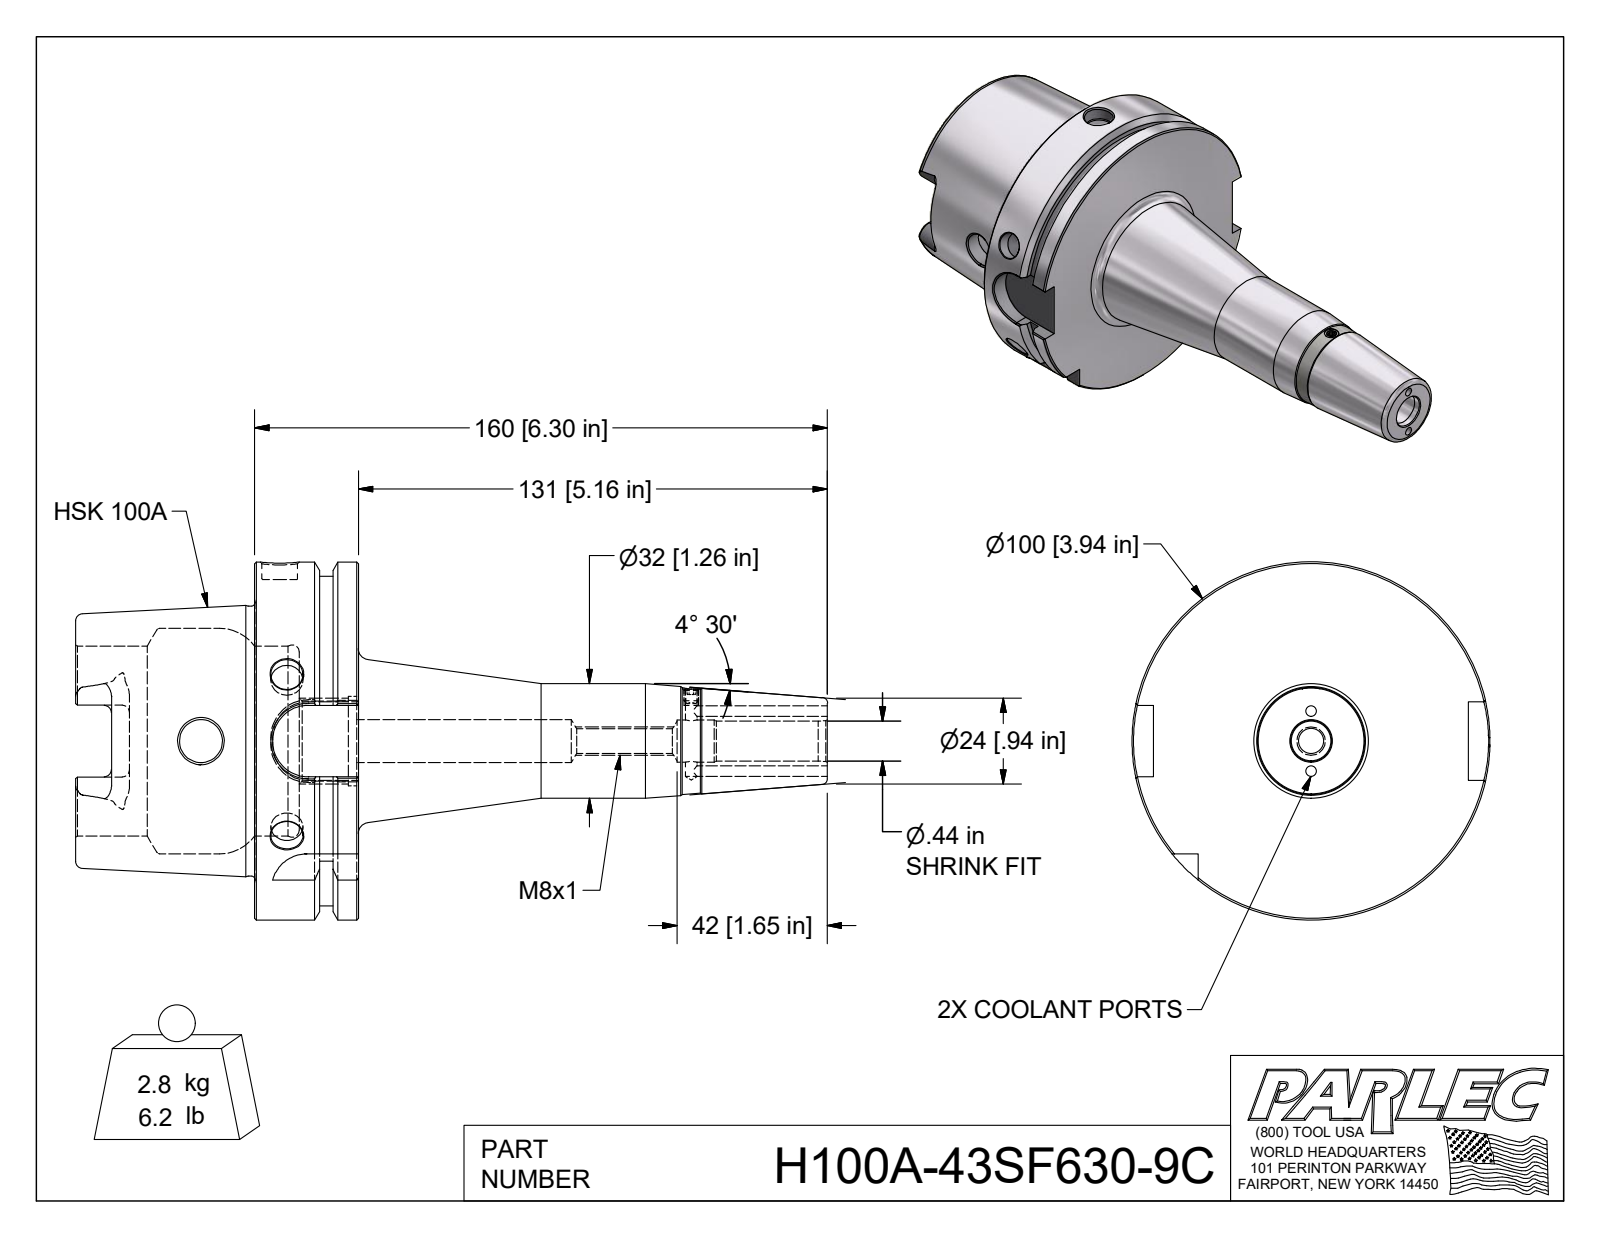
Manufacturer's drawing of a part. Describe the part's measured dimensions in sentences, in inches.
Its 3-D file was written by "Autodesk Inventor 2018 (AUTOMOTIVE_DESIGN)". It is 1 solid with 157 faces: 50 planar, 43 cylindrical and 64 other. Overall it measures 8.268 by 3.937 by 3.937 inches. Its volume is 21.86 cubic inches and its surface area 104.6 square inches. Round holes: 2 of diameter 0.118, 2 of diameter 0.354, 2 of diameter 0.472, 1 of diameter 0.128, 1 of diameter 0.197, 1 of diameter 0.272, 1 of diameter 0.394, 1 of diameter 0.437, 1 of diameter 0.467, 1 of diameter 0.472, 1 of diameter 0.881, 1 of diameter 0.985. Round bosses or shafts: 1 of diameter 3.937, 1 of diameter 3.622, 1 of diameter 2.967, 1 of diameter 1.26. Partial cylindrical surfaces (rounded edges, fillets, slot ends): 6 of radius 0.079, 4 of radius 0.192, 4 of radius 0.394. The main face-to-face distances are 1.142, 0.492, 0.65, 1.969, 2.461, 3.11, 3.465, 2.83, 0.861, 0.369. The hole center spacings are 0.33, 0.66, 4.528.
